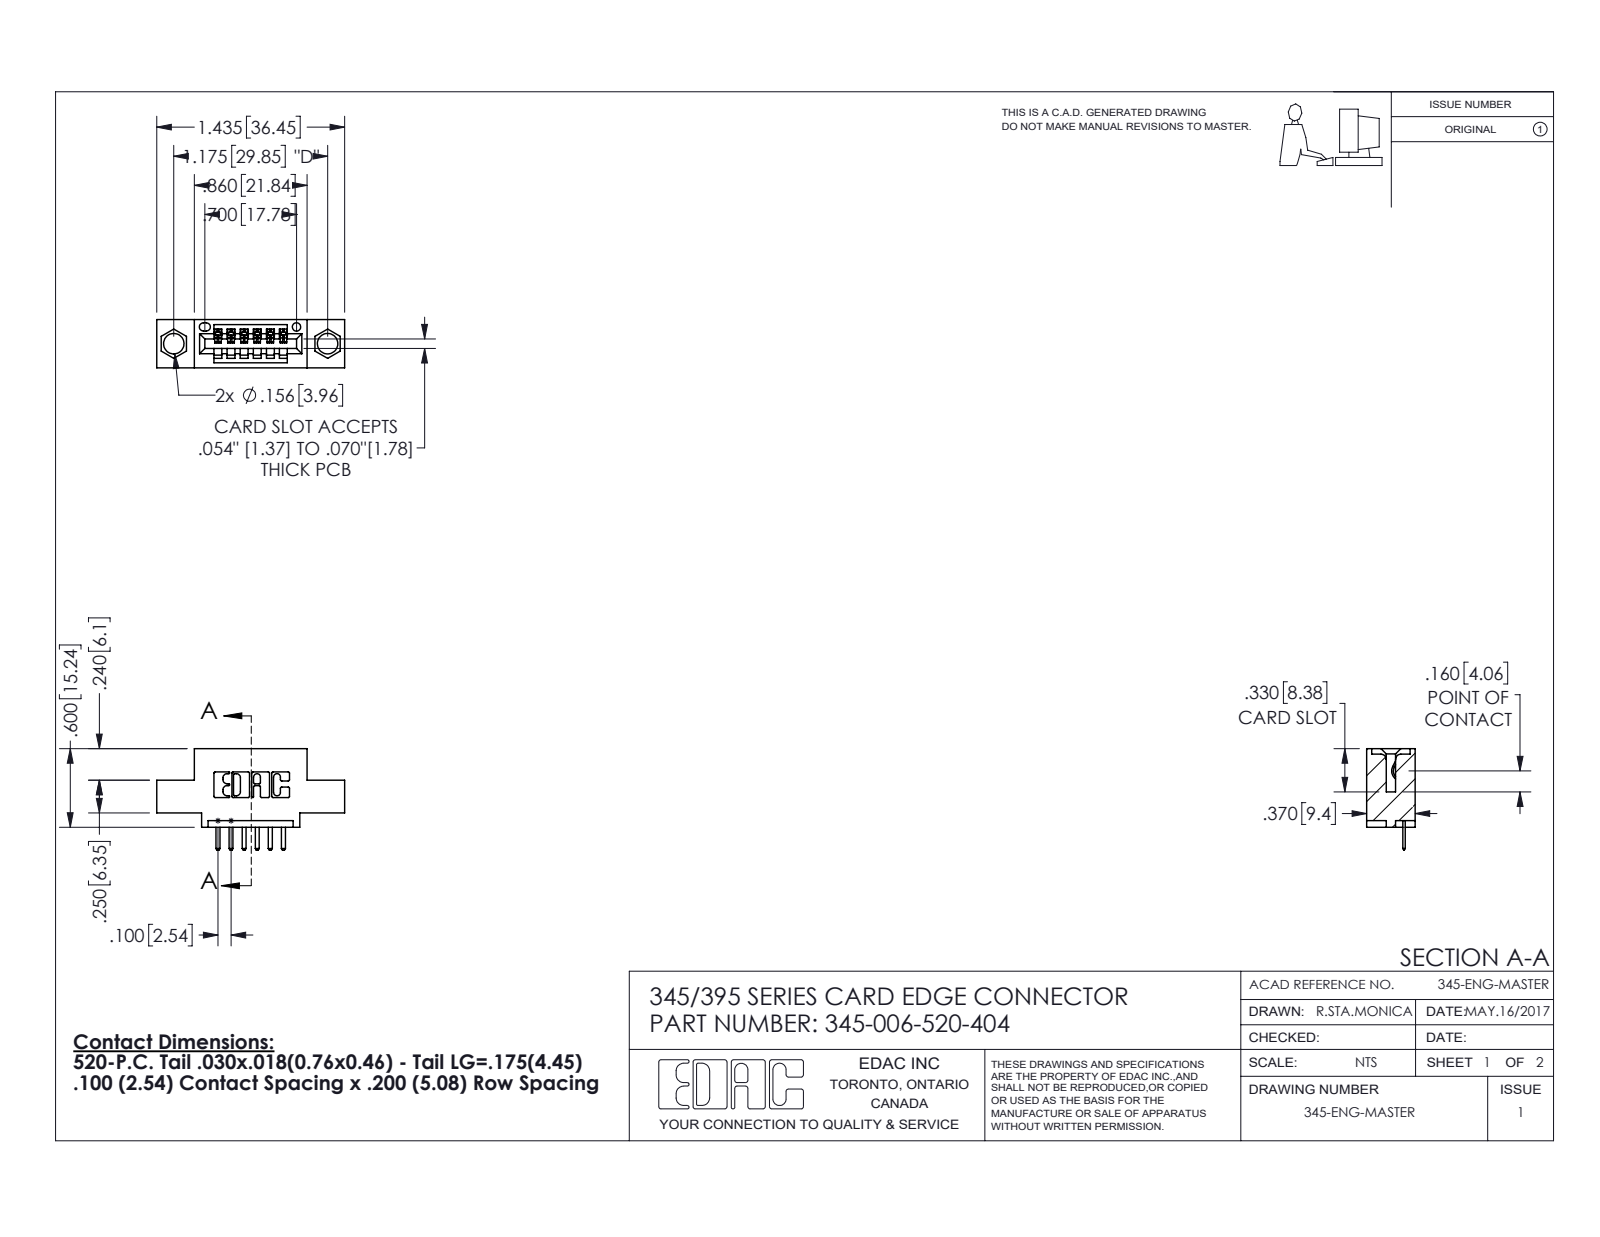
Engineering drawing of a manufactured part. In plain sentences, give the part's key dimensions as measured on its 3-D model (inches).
The part is named "345-006-520-404; 345-292-001_345-293-120; 345 Part_0.110 Offset - 0.156 Dia-TH". Its 3-D file was written by "SolidWorks 2016 (CONFIG_CONTROL_DESIGN)". It is 7 solids with 502 faces: 336 planar, 166 cylindrical and 0 other. Overall it measures 1.435 by 0.775 by 0.37 inches. Its volume is 0.182 cubic inches and its surface area 5.141 square inches. Round holes: 2 of diameter 0.156, 1 of diameter 0.064. Partial cylindrical surfaces (rounded edges, fillets, slot ends): 22 of radius 0.01, 14 of radius 0.01, 12 of radius 0.006, 6 of radius 0.007, 6 of radius 0.031, 3 of radius 0.026, 2 of radius 0.031, 2 of radius 0.04. The main face-to-face distances are 0.2, 0.37, 0.1, 0.298, 0.072, 0.16, 0.06, 0.3, 0.025, 0.25. The hole center spacings are 0.27, 0.946, 1.175.
